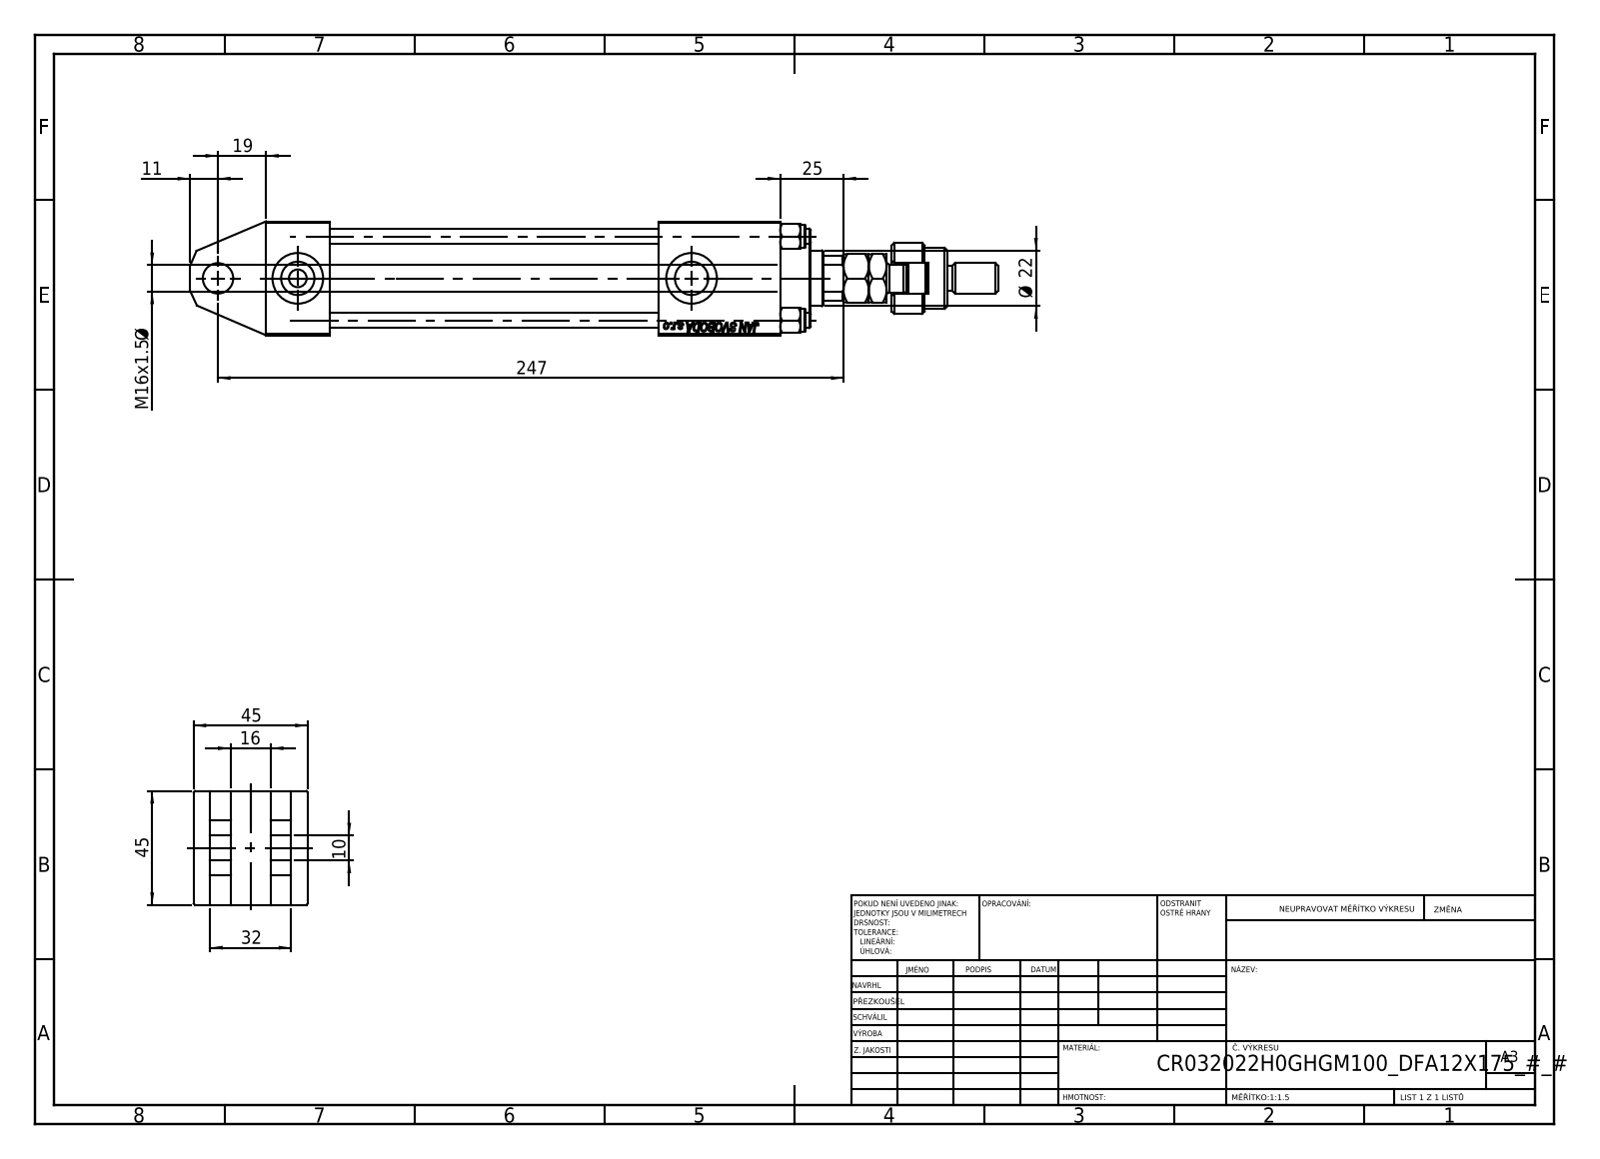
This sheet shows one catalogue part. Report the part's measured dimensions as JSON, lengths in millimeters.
{"part_name": "V215CR_H_Body; NUT_M5_H; V215CR_VCP_H; MFA (+3 more)", "step_written_by": "SolidWorks 2019 (CONFIG_CONTROL_DESIGN)", "units": "millimeters", "bodies": {"solids": 13, "faces": 1213, "planar": 545, "cylindrical": 96, "other": 572}, "overall_size": [319, 45, 45], "volume_mm3": 308896, "surface_area_mm2": 114633, "round_holes": [[6, 4], [7, 2], [13.16, 2], [20, 2], [10.5, 1], [12, 1], [22, 1], [24, 1], [25, 1], [32, 1], [33, 1]], "round_bosses_or_shafts": [[9, 4], [38, 1], [34, 1], [28, 1], [18, 1], [12, 1], [11, 1], [10, 1]], "partial_cylinders_radius": [[9.75, 1], [10.5, 1]], "face_to_face_distances": [45, 8, 25, 14.5, 38.5, 24, 30.5, 203, 6.5, 32], "hole_center_spacings": [23.48, 33.2, 46.95, 31.5, 155.5, 187]}
